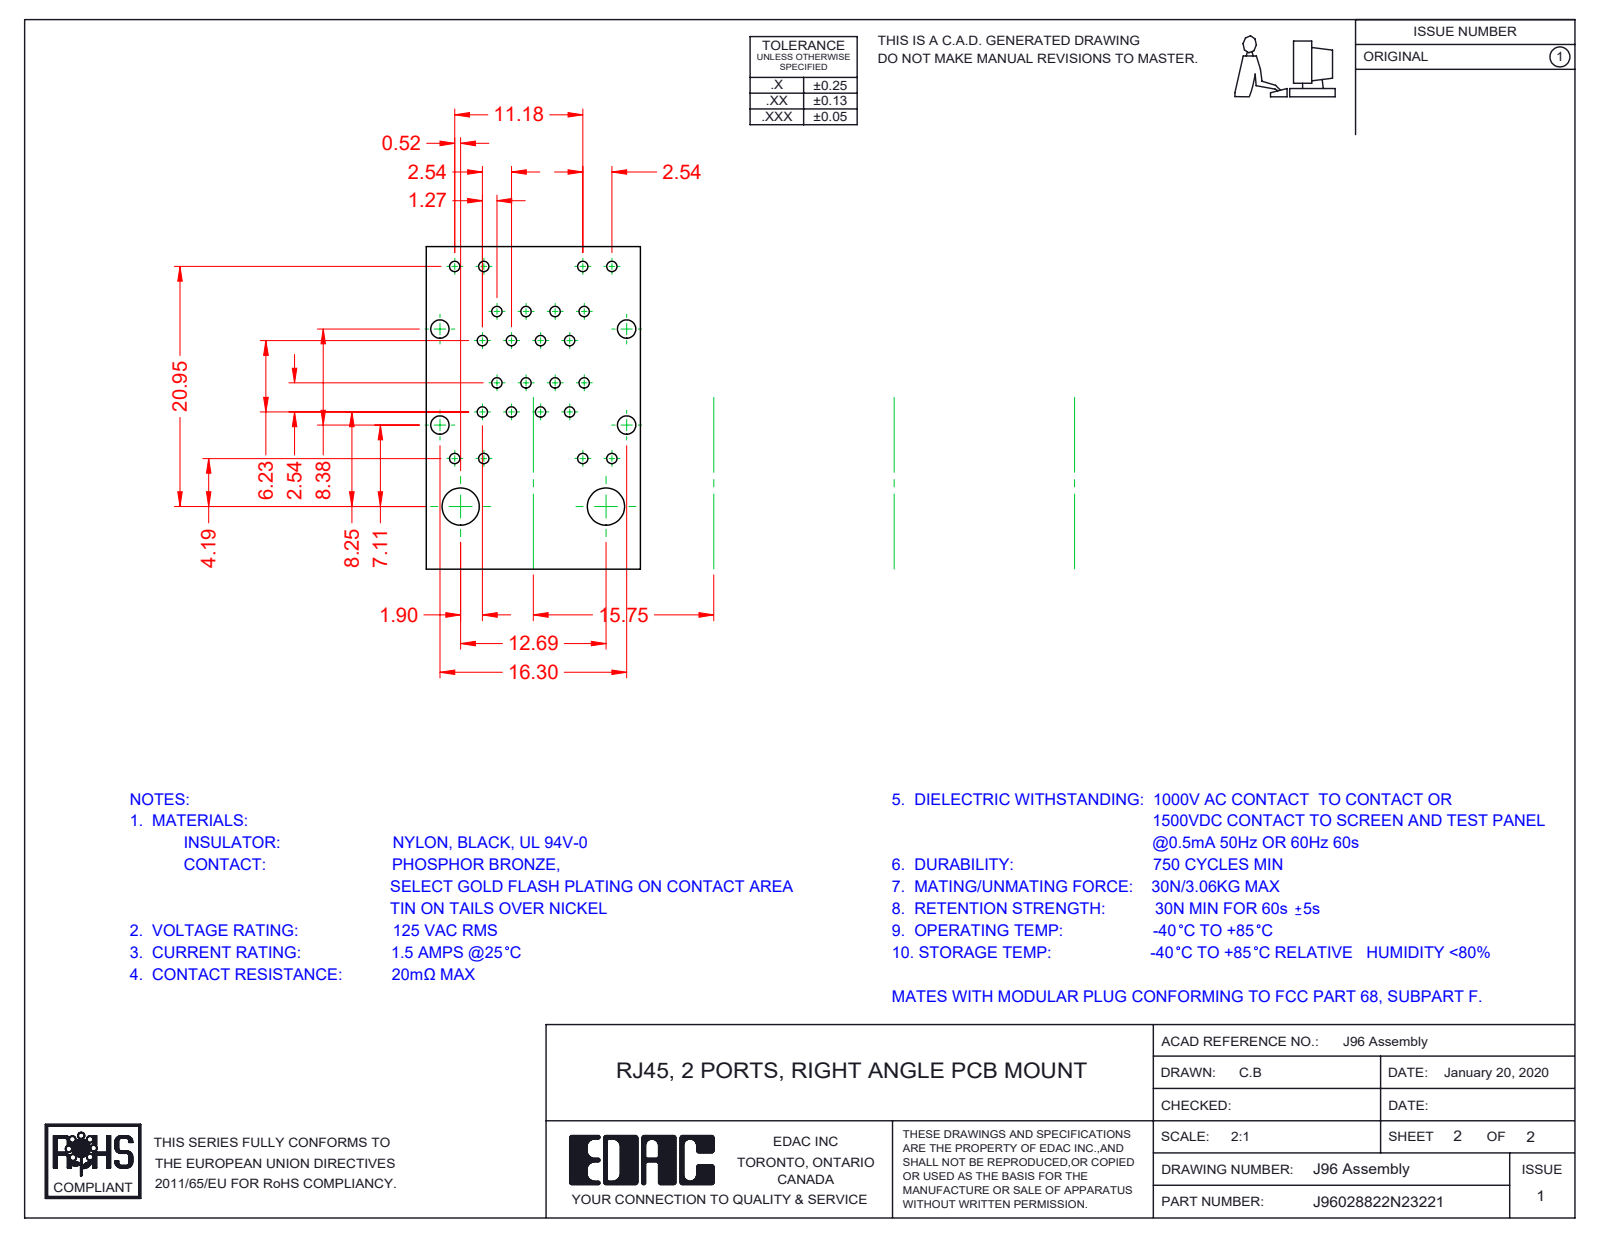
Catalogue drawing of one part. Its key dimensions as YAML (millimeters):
part_name: "96 LED LH Upper_2-Red; 96 Contacts Lower; J96028822N23221; 96 Shield_2 Ports LED - EMI (+8 more)"
step_written_by: "SolidWorks 2016 (CONFIG_CONTROL_DESIGN)"
units: millimeters
bodies: {solids: 27, faces: 2417, planar: 1865, cylindrical: 446, other: 106}
overall_size: [31.38, 28.68, 16.8]
volume: 6849
surface_area: 19094
partial_cylinders:
  - {radius: 0.25, count: 48}
  - {radius: 0.15, count: 32}
  - {radius: 0.35, count: 24}
  - {radius: 0.5, count: 16}
  - {radius: 1, count: 16}
  - {radius: 0.2, count: 14}
  - {radius: 0.7, count: 9}
  - {radius: 2, count: 5}
face_to_face_distances: [16.3, 16.1, 1.75, 16.5, 14.75, 1.55, 14.55, 0.53, 1.48, 11.2]
